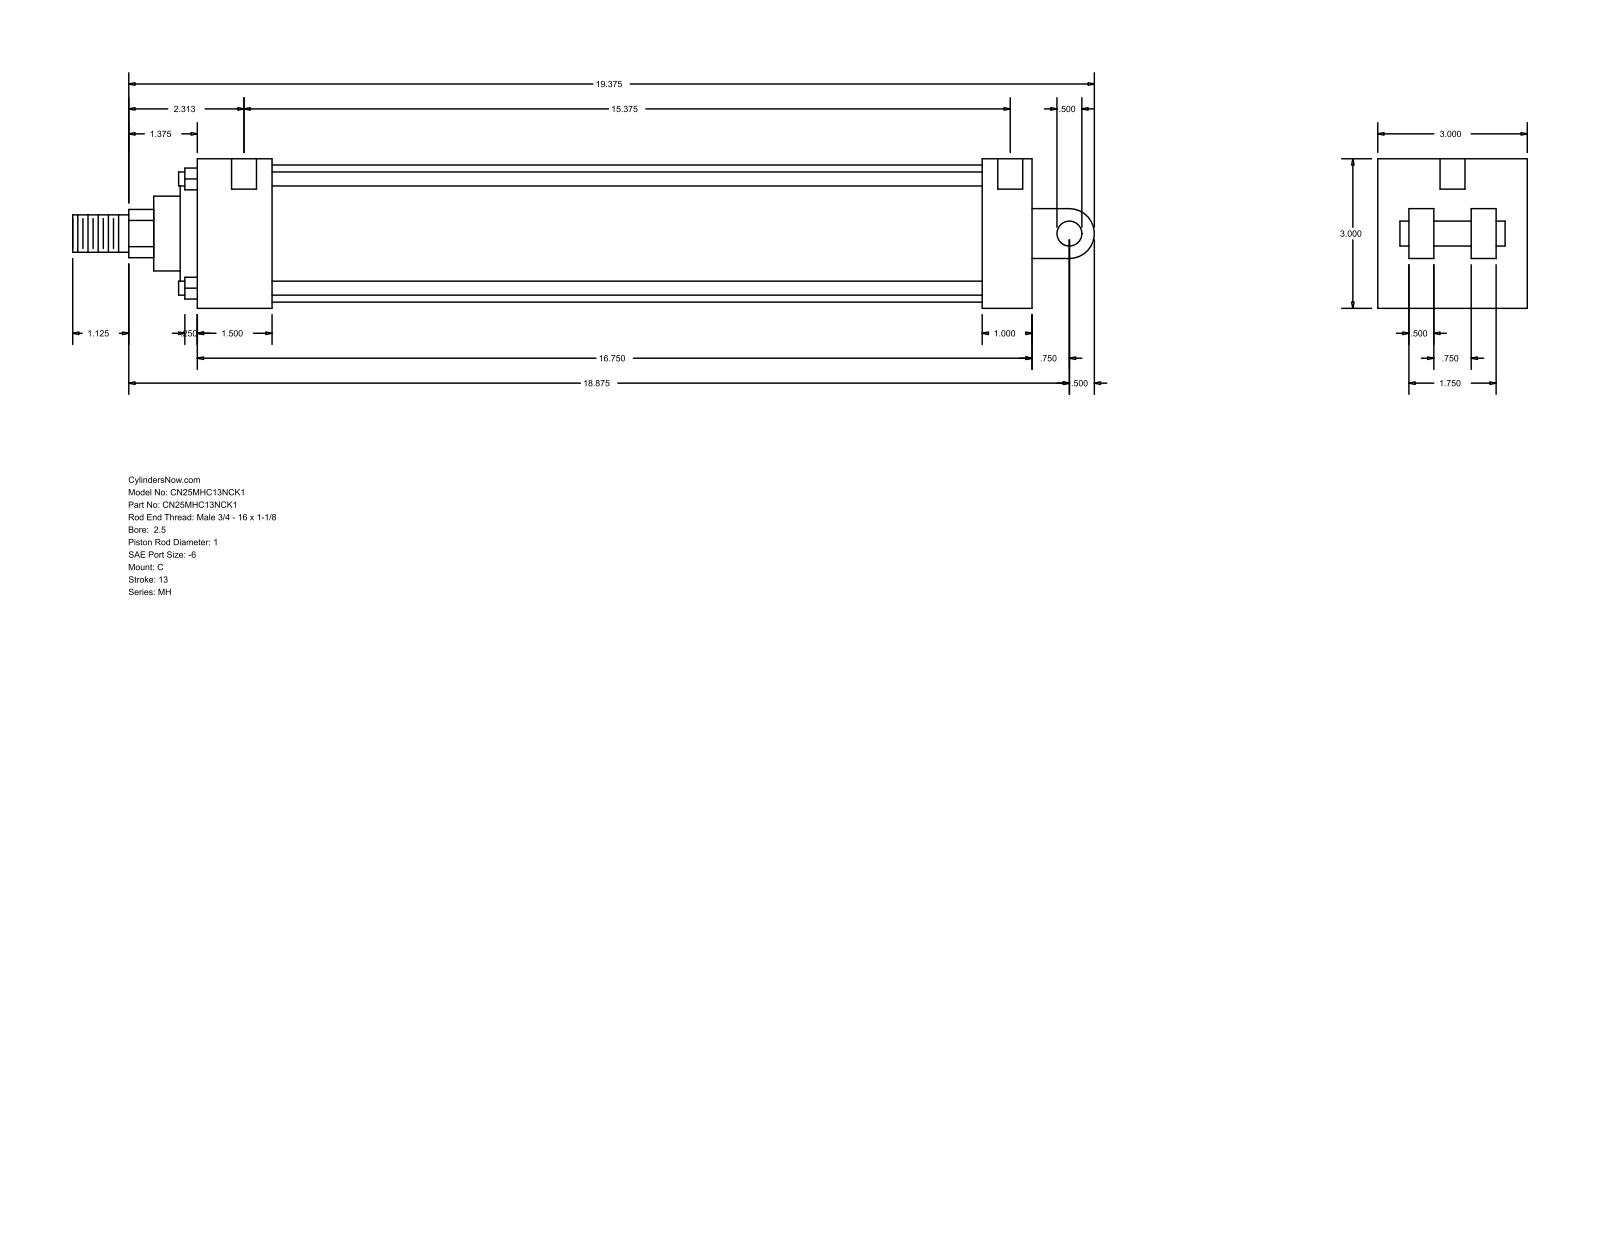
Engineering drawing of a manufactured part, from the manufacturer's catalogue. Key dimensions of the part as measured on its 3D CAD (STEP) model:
Part name (STEP PRODUCT): MH_C__0250_1
STEP written by: GSSL Pune (CONFIG_CONTROL_DESIGN)
Units: millimetres
Bodies: 0 solids, 101 faces (71 planar, 30 cylindrical, 0 other)
Overall size (bounding box): 520.7 × 76.2 × 76.2
Round holes (diameter × count): ⌀5.56 ×4, ⌀12.7 ×2
Round bosses / shafts (diameter × count): ⌀7.14 ×4, ⌀69.85 ×1, ⌀60.33 ×1, ⌀38.1 ×1, ⌀25.4 ×1, ⌀19.05 ×1, ⌀12.7 ×1
Partial cylindrical surfaces — rounded edges, fillets, slot ends (radius × count): R12.29 ×1, R12.7 ×1
Main face-to-face distances: 76.2, 25.4, 425.46, 60.33, 15.87, 400.06, 38.11, 361.95, 387.35, 12.7
Hole centre spacings: 398.46, 3.18, 4.76, 390.52, 393.7, 395.28
